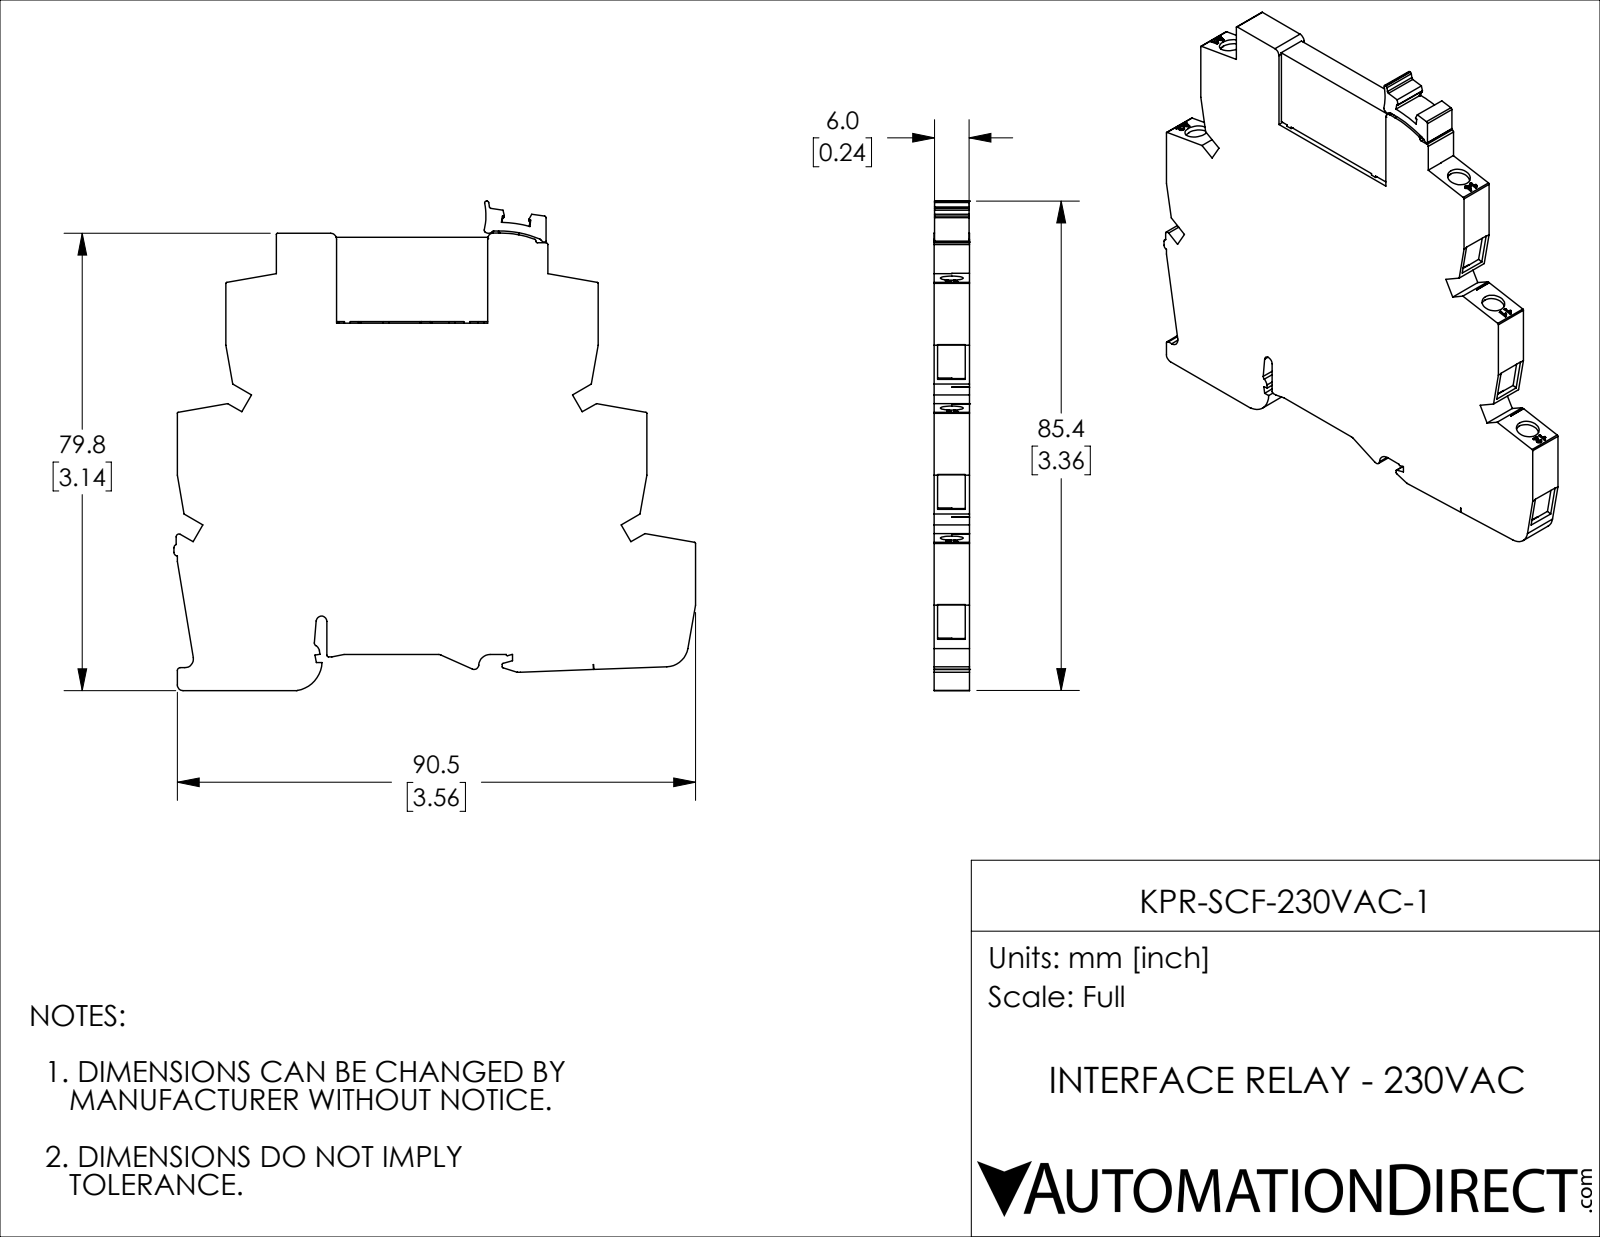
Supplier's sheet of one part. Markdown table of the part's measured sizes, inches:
| quantity | value |
| --- | --- |
| part name | KPR-SCF-230VAC-1 |
| STEP written by | SolidWorks 2018 (AUTOMOTIVE_DESIGN) |
| units | inches |
| bodies | 1 solid, 422 faces (304 planar, 90 cylindrical, 28 other) |
| overall size | 3.586 × 3.364 × 0.244 |
| volume | 2.104 in³ |
| surface area | 23.55 in² |
| round holes (diameter × count) | 0.157 × 5 |
| round bosses / shafts (diameter × count) | 0.016 × 2 |
| partial cylindrical surfaces (radius × count) | 0.008 × 15, 0.012 × 10, 0.039 × 10, 0.02 × 5, 0.037 × 5, 0.079 × 3, 0.004 × 2, 0.024 × 2 |
| main face-to-face distances | 0.244, 0.024, 0.22, 0.033, 0.197, 0.335, 0.031, 0.821, 3.228, 2.894 |
| hole center spacings | 0.485, 0.485, 0.969 |
